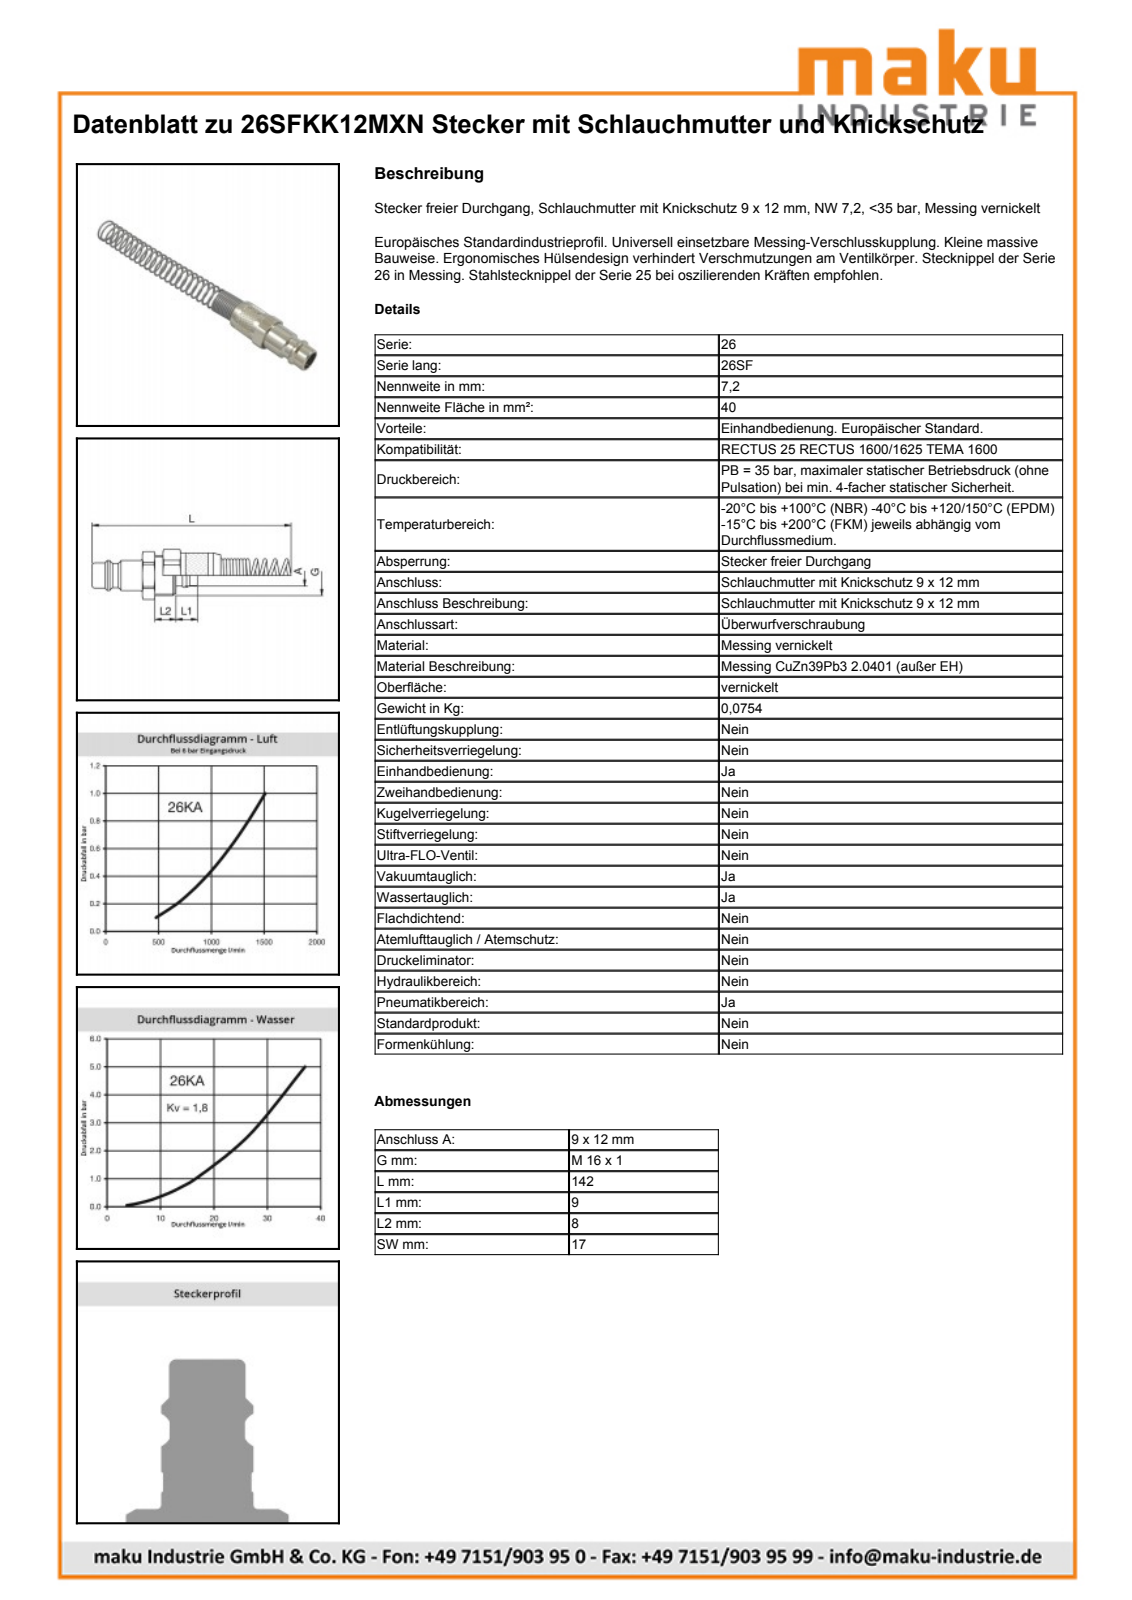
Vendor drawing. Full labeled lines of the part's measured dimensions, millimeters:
Part name (STEP PRODUCT): D103137; D103133; D103135; D103136
STEP written by: Autodesk Inventor 2011 (AUTOMOTIVE_DESIGN)
Units: millimetres
Bodies: 3 solids, 95 faces (27 planar, 29 cylindrical, 39 other)
Overall size (bounding box): 143.4 × 20.75 × 19
Volume: 9 760 mm³ · Surface area: 15 293 mm²
Round holes (diameter × count): ⌀6.9 ×1, ⌀7.85 ×1, ⌀12.25 ×1, ⌀14.92 ×1, ⌀15.25 ×1
Round bosses / shafts (diameter × count): ⌀19 ×1, ⌀18.98 ×1, ⌀16 ×1, ⌀14.6 ×1, ⌀12 ×1, ⌀11 ×1, ⌀10 ×1, ⌀9.75 ×1
Partial cylindrical surfaces — rounded edges, fillets, slot ends (radius × count): R9.57 ×1, R10.38 ×1
Main face-to-face distances: 18, 1, 19, 17, 8, 5.4, 13.4, 3, 23, 9
